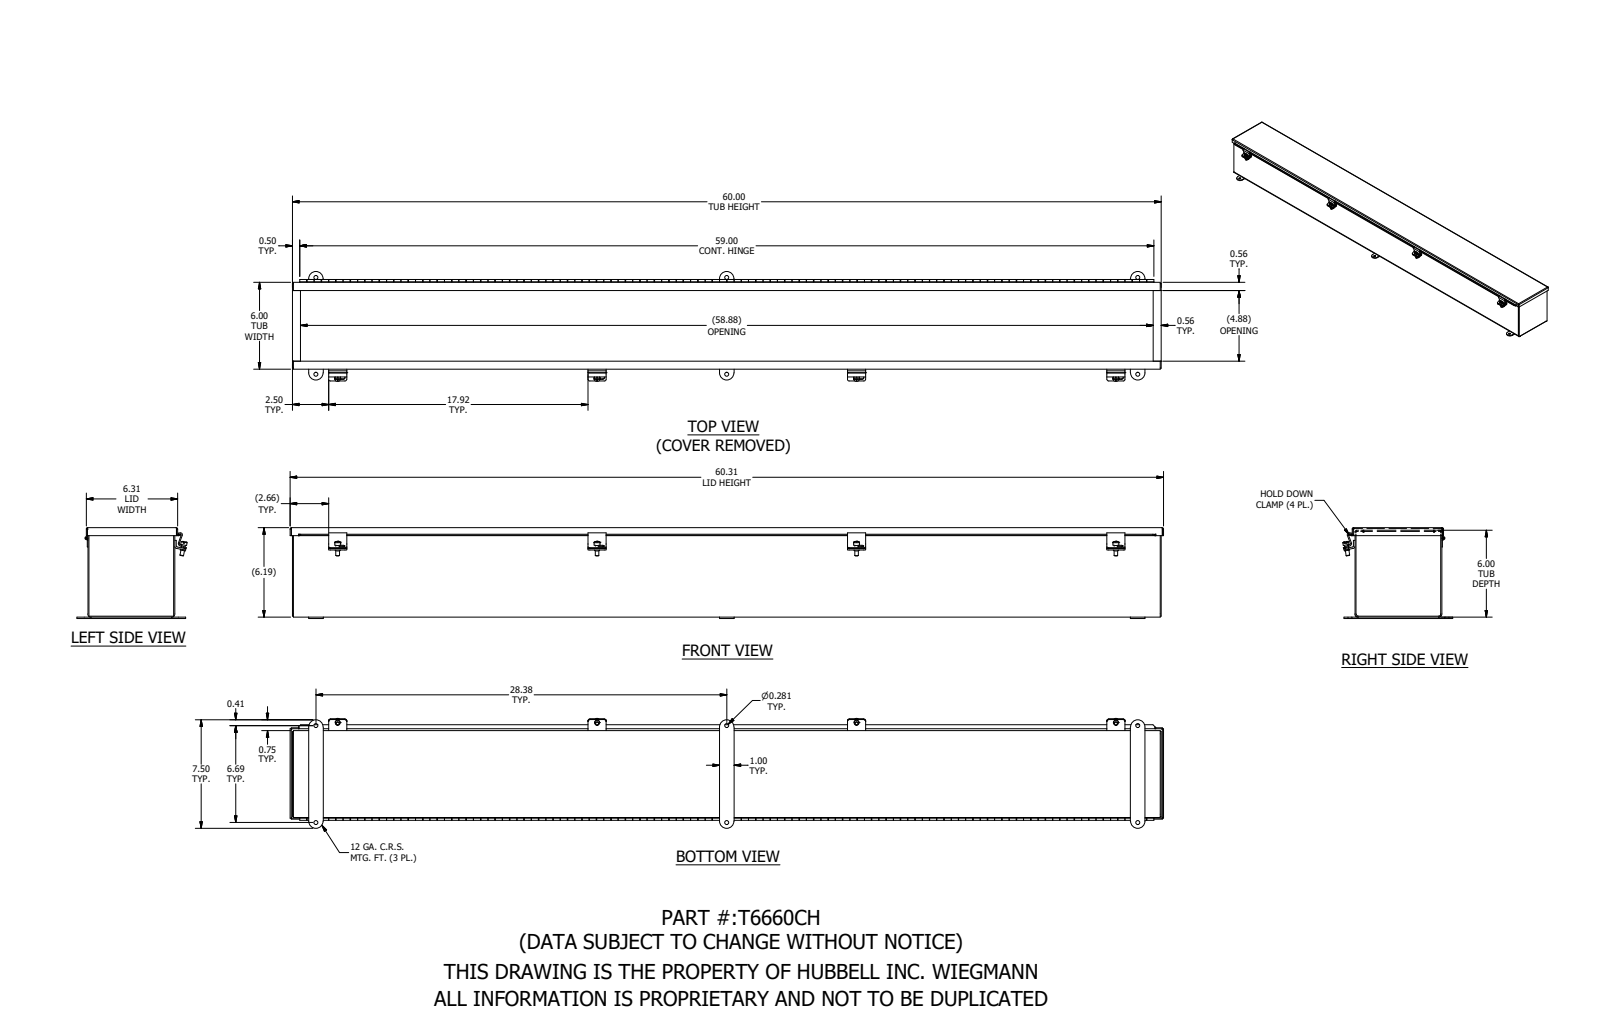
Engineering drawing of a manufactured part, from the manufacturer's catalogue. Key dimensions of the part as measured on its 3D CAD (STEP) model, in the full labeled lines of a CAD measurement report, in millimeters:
Part name (STEP PRODUCT): T6660CH
STEP written by: SolidWorks 2021 (AUTOMOTIVE_DESIGN)
Units: millimetres
Bodies: 22 solids, 1221 faces (592 planar, 601 cylindrical, 28 other)
Overall size (bounding box): 1532 × 192.9 × 159.6
Volume: 2 112 000 mm³ · Surface area: 2 318 000 mm²
Round holes (diameter × count): ⌀7.1 ×6, ⌀5 ×4, ⌀2.9 ×1
Round bosses / shafts (diameter × count): ⌀10.4 ×4, ⌀8.7 ×4, ⌀6.4 ×4, ⌀5.1 ×1, ⌀2.5 ×1
Partial cylindrical surfaces — rounded edges, fillets, slot ends (radius × count): R3.2 ×16, R0.8 ×9, R2.7 ×9, R3.4 ×8, R12.7 ×6, R1.6 ×3, R3.2 ×3, R4 ×2
Main face-to-face distances: 1.9, 150.5, 155.3, 152.4, 148.6, 157.2, 153.4, 4.8, 2.9, 153.5
Hole centre spacings: 169.8, 455.1, 720.7, 720.7, 740.5, 740.5, 1441.5, 1451.4
